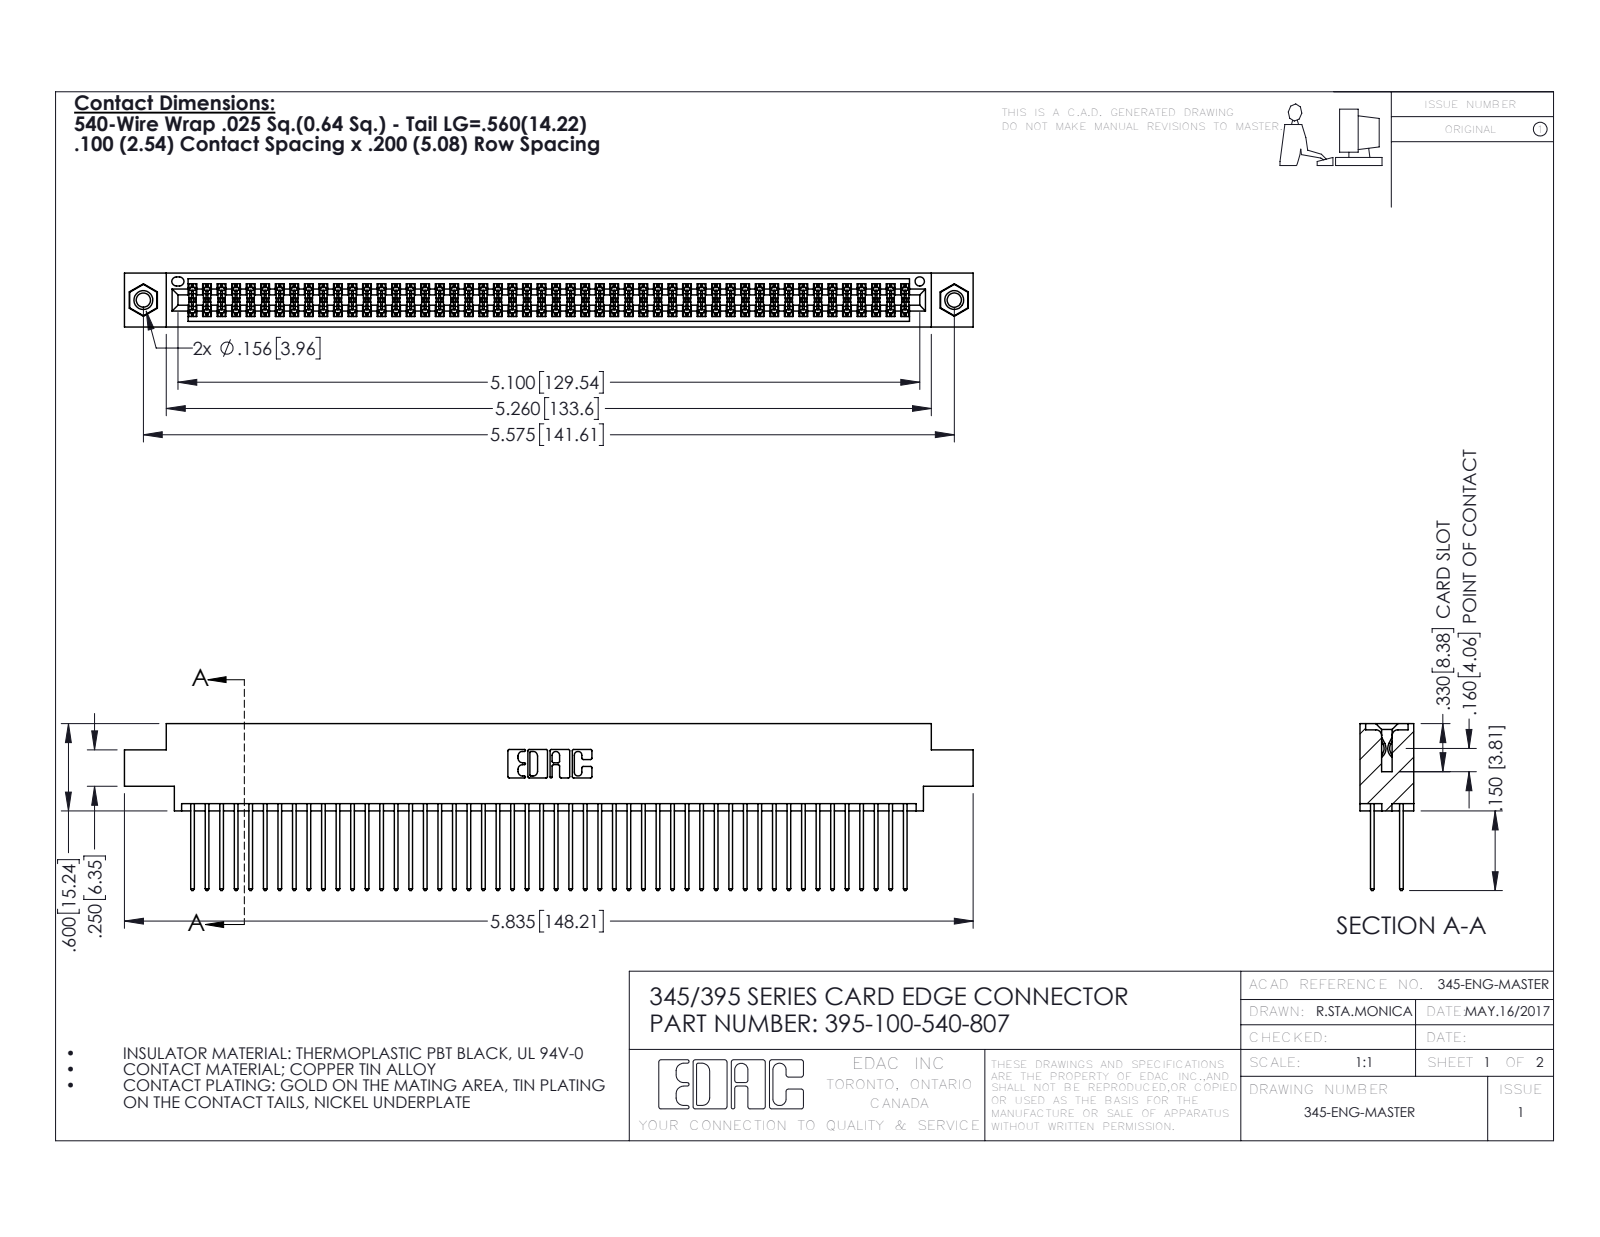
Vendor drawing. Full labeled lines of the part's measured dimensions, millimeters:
Part name (STEP PRODUCT): 395-100-540-807; 345-292-001_345-293-140; 345-250-001_345-250-005-103; 345 Part_0.170 Offset - 0.156 Dia-TI
STEP written by: SolidWorks 2016 (CONFIG_CONTROL_DESIGN)
Units: millimetres
Bodies: 103 solids, 5190 faces (3416 planar, 1758 cylindrical, 16 other)
Overall size (bounding box): 148.2 × 29.1 × 9.4
Volume: 14 700 mm³ · Surface area: 23 850 mm²
Round holes (diameter × count): ⌀2.5 ×2, ⌀3.2 ×2, ⌀4 ×2, ⌀1.6 ×1
Round bosses / shafts (diameter × count): ⌀3.9 ×2
Partial cylindrical surfaces — rounded edges, fillets, slot ends (radius × count): R0.2 ×150, R0.3 ×100, R0.3 ×22, R0.2 ×6, R0.8 ×6, R0.7 ×3, R0.4 ×2, R0.5 ×2
Main face-to-face distances: 1.8, 7.6, 5.1, 2.5, 6.9, 0.6, 9.4, 5.7, 4.4, 3.8
Hole centre spacings: 6.9, 135.6, 141.6
